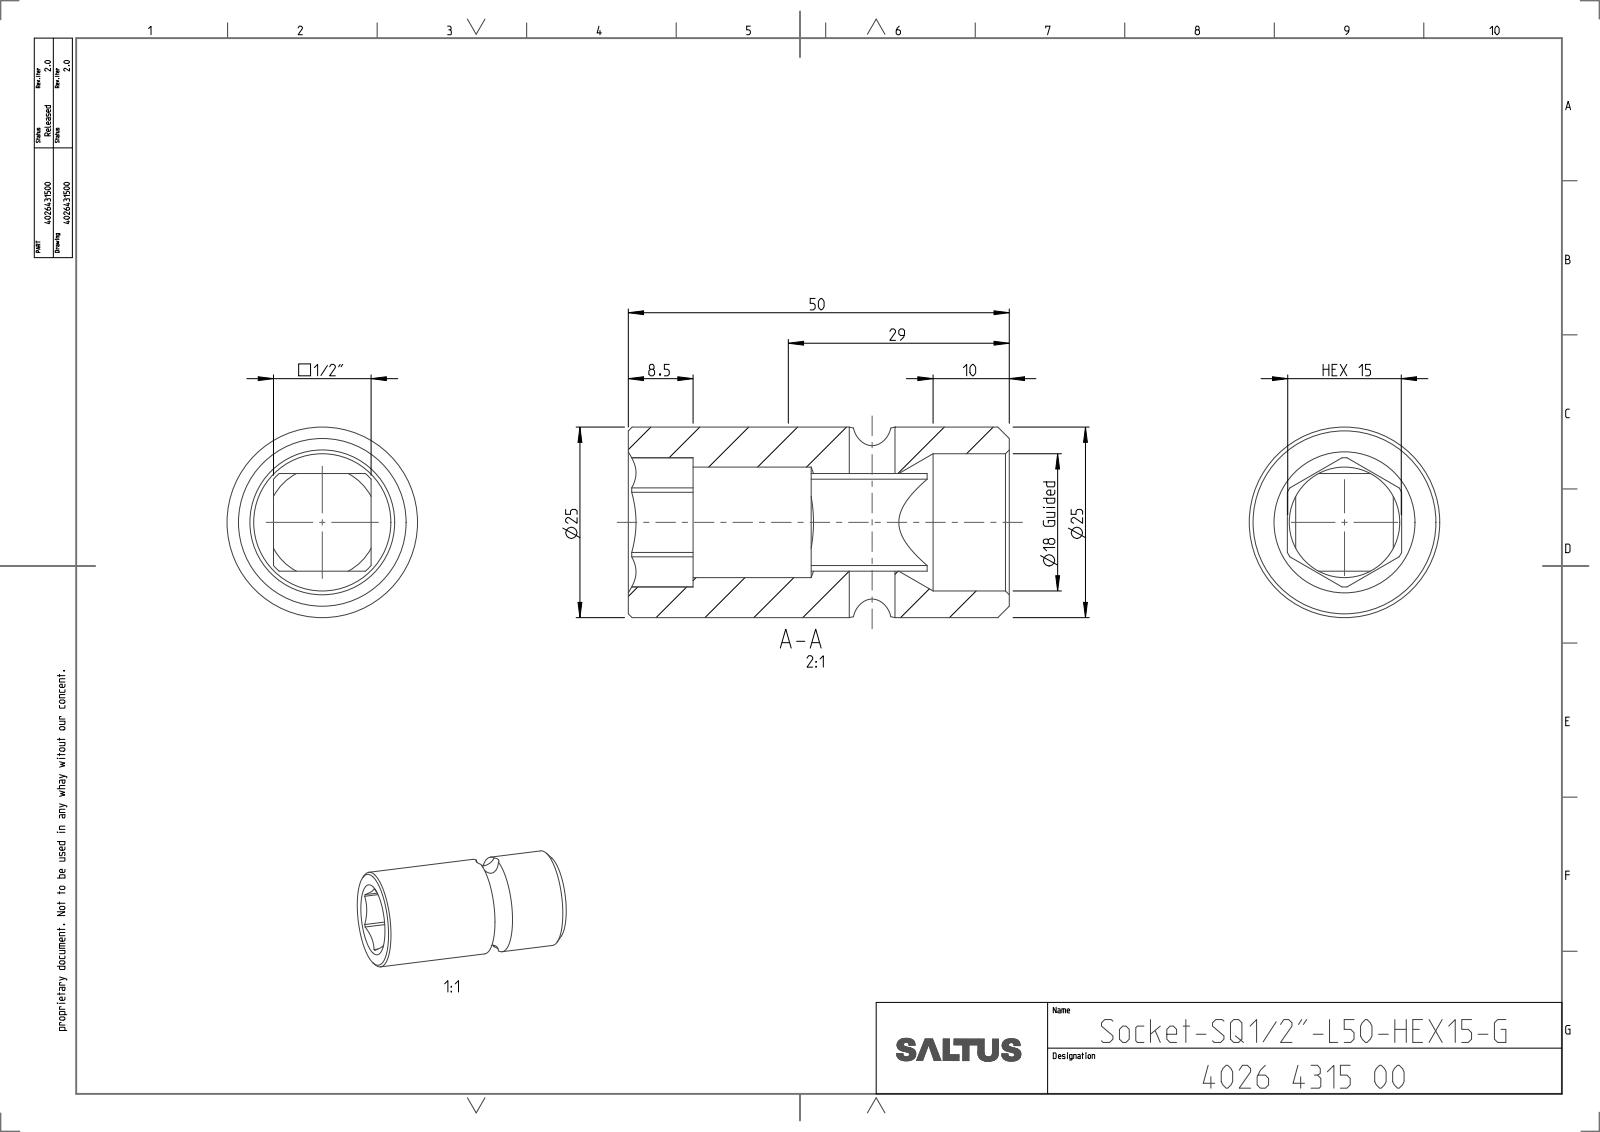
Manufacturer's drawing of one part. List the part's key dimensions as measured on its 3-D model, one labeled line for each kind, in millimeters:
Part name (STEP PRODUCT): 4026431500
STEP written by: CREO PARAMETRIC BY PTC INC, 2022414 (CONFIG_CONTROL_DESIGN)
Units: millimetres
Bodies: 1 solid, 56 faces (17 planar, 23 cylindrical, 16 other)
Overall size (bounding box): 50 × 25 × 25
Volume: 14 090 mm³ · Surface area: 7 065 mm²
Round holes (diameter × count): ⌀6 ×1, ⌀14.5 ×1, ⌀18 ×1
Round bosses / shafts (diameter × count): ⌀25 ×1
Partial cylindrical surfaces — rounded edges, fillets, slot ends (radius × count): R8.47 ×1, R8.55 ×1
Main face-to-face distances: 12.82, 15, 1.09, 13.91, 50, 41.5, 8.5, 26, 15.5, 24
